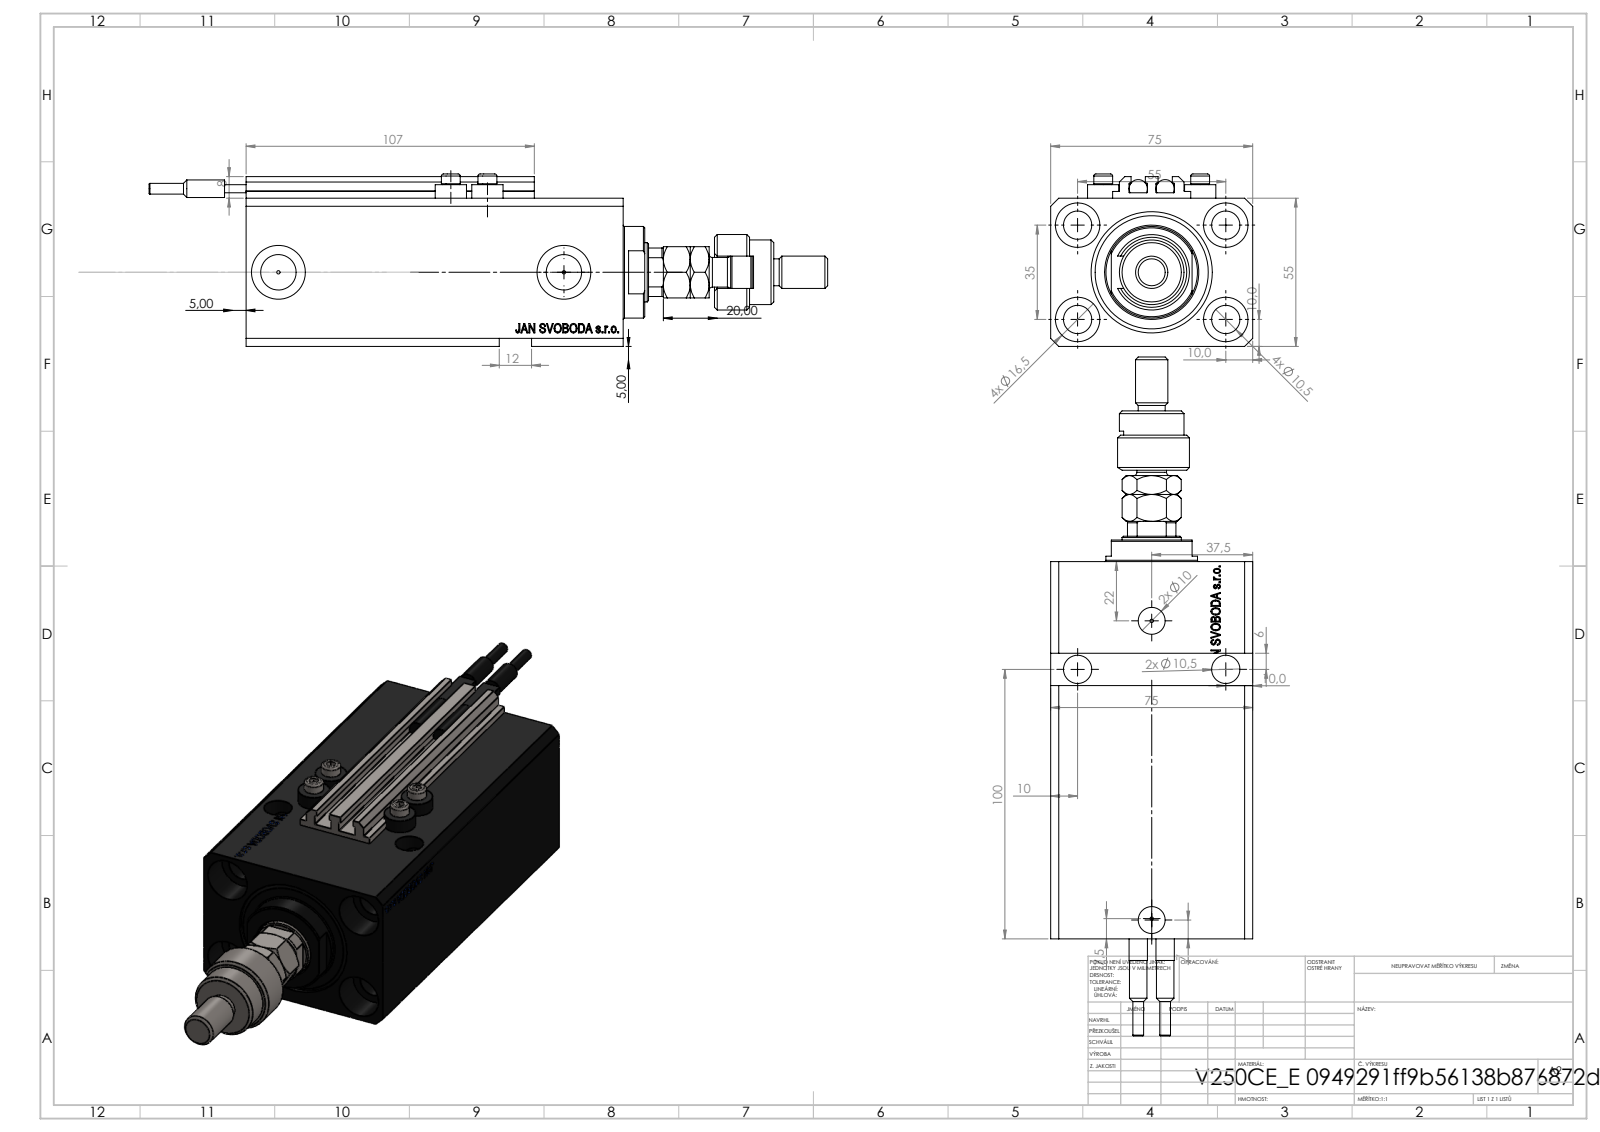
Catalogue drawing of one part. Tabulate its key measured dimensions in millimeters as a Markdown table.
| quantity | value |
| --- | --- |
| part name | MFA; V250CE_E_Body; SWITCH_V250CE; V250CE_VC_E (+3 more) |
| STEP written by | SolidWorks 2019 (CONFIG_CONTROL_DESIGN) |
| units | millimeters |
| bodies | 12 solids, 1221 faces (574 planar, 171 cylindrical, 476 other) |
| overall size | 252 × 75 × 64 |
| volume | 506 672 mm³ |
| surface area | 125 175 mm² |
| round holes (diameter × count) | 10.5 × 9, 1.25 × 4, 4 × 4, 16.5 × 4, 10 × 2, 13.16 × 2, 20 × 2, 22 × 1, 32 × 1, 45 × 1 |
| round bosses / shafts (diameter × count) | 11.6 × 4, 7 × 4, 6.8 × 2, 6.5 × 2, 4 × 2, 34 × 1, 28 × 1, 24 × 1 |
| partial cylindrical surfaces (radius × count) | 0.2 × 10, 9.75 × 1, 10.5 × 1 |
| main face-to-face distances | 55, 75, 15, 3, 57, 140, 8, 125, 9.9, 2 |
| hole center spacings | 32.6, 32.87, 55, 96.98, 13.6, 14.09, 25.81, 32.58 |
